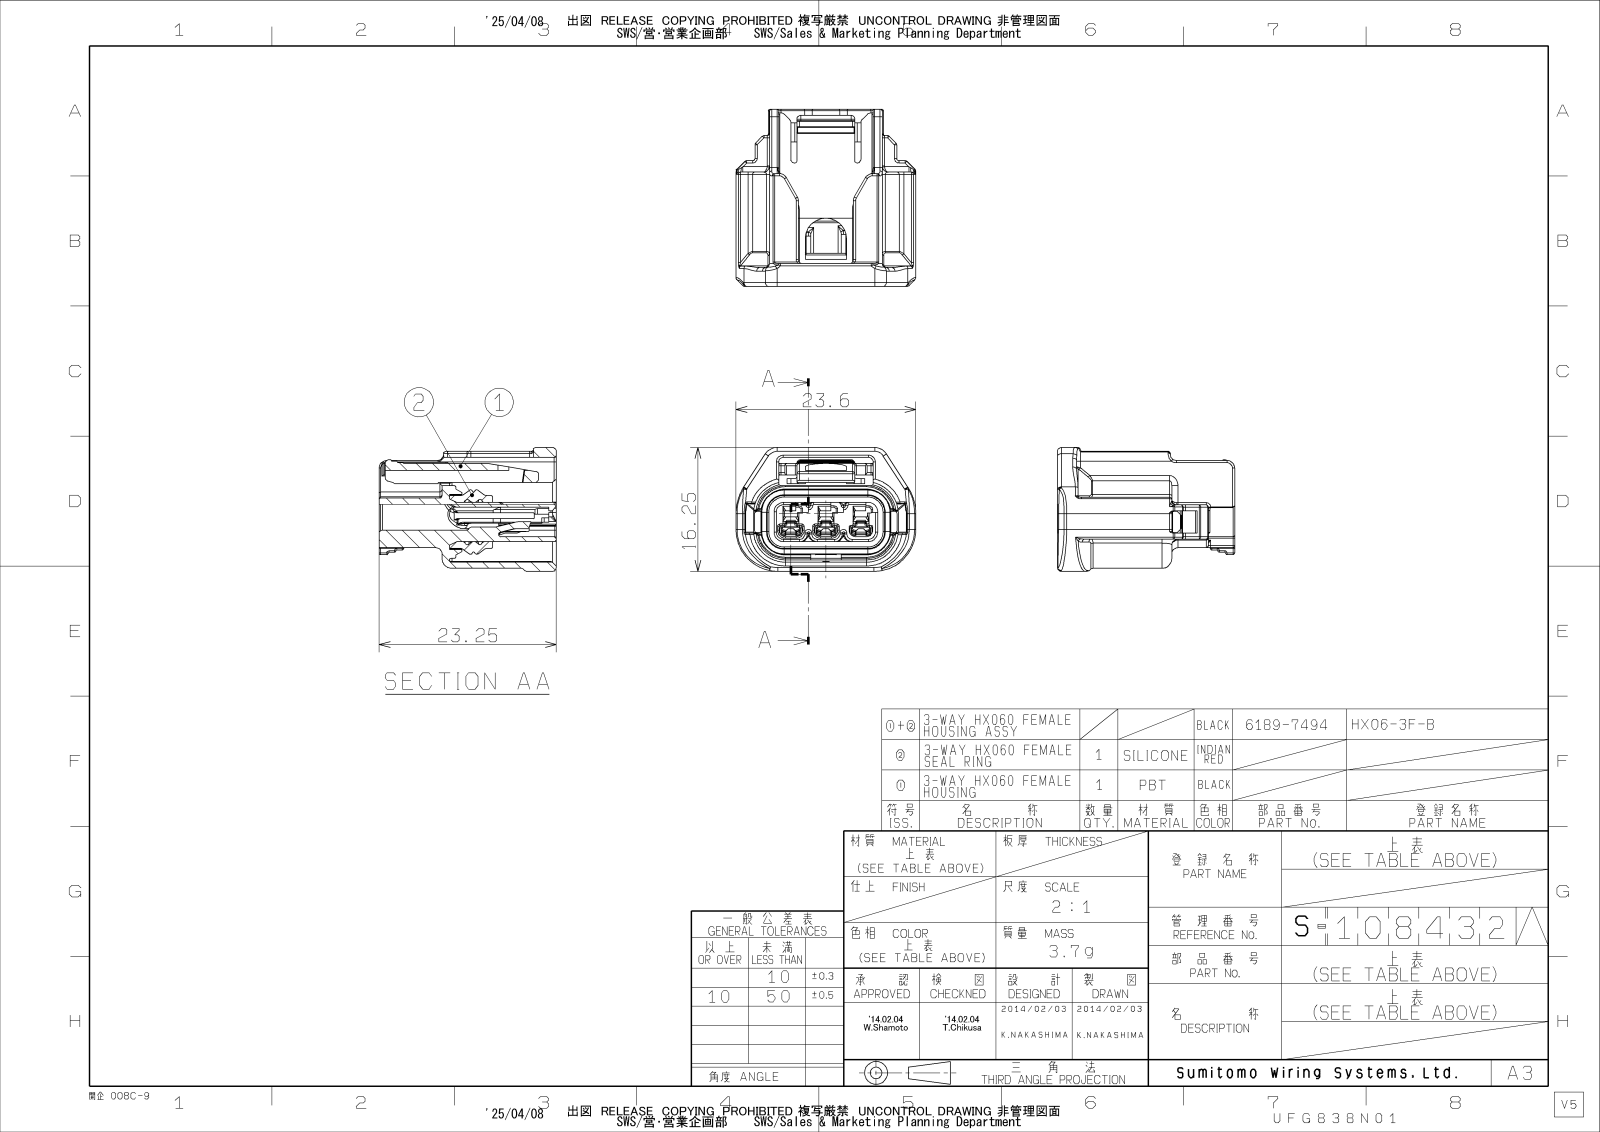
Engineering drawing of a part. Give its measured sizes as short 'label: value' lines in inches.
name: 6189-7494
written by: CATIA V5 STEP AP214 v2 (AUTOMOTIVE_DESIGN)
unit: in
bodies: 1 solid, 260 faces (182 planar, 66 cylindrical, 12 other)
size: 0.929 × 0.915 × 0.64
volume: 0.204 in³; area: 6.251 in²
holes: 3× ⌀0.161
rounds: 5× R0.039, 4× R0.004, 4× R0.02, 4× R0.049, 4× R0.059, 4× R0.071, 4× R0.165, 4× R0.197
face distances: 0.047, 0.031, 0.535, 0.138, 0.024, 0.106, 0.203, 0.309, 0.031, 0.325
hole spacings: 0.181, 0.362
